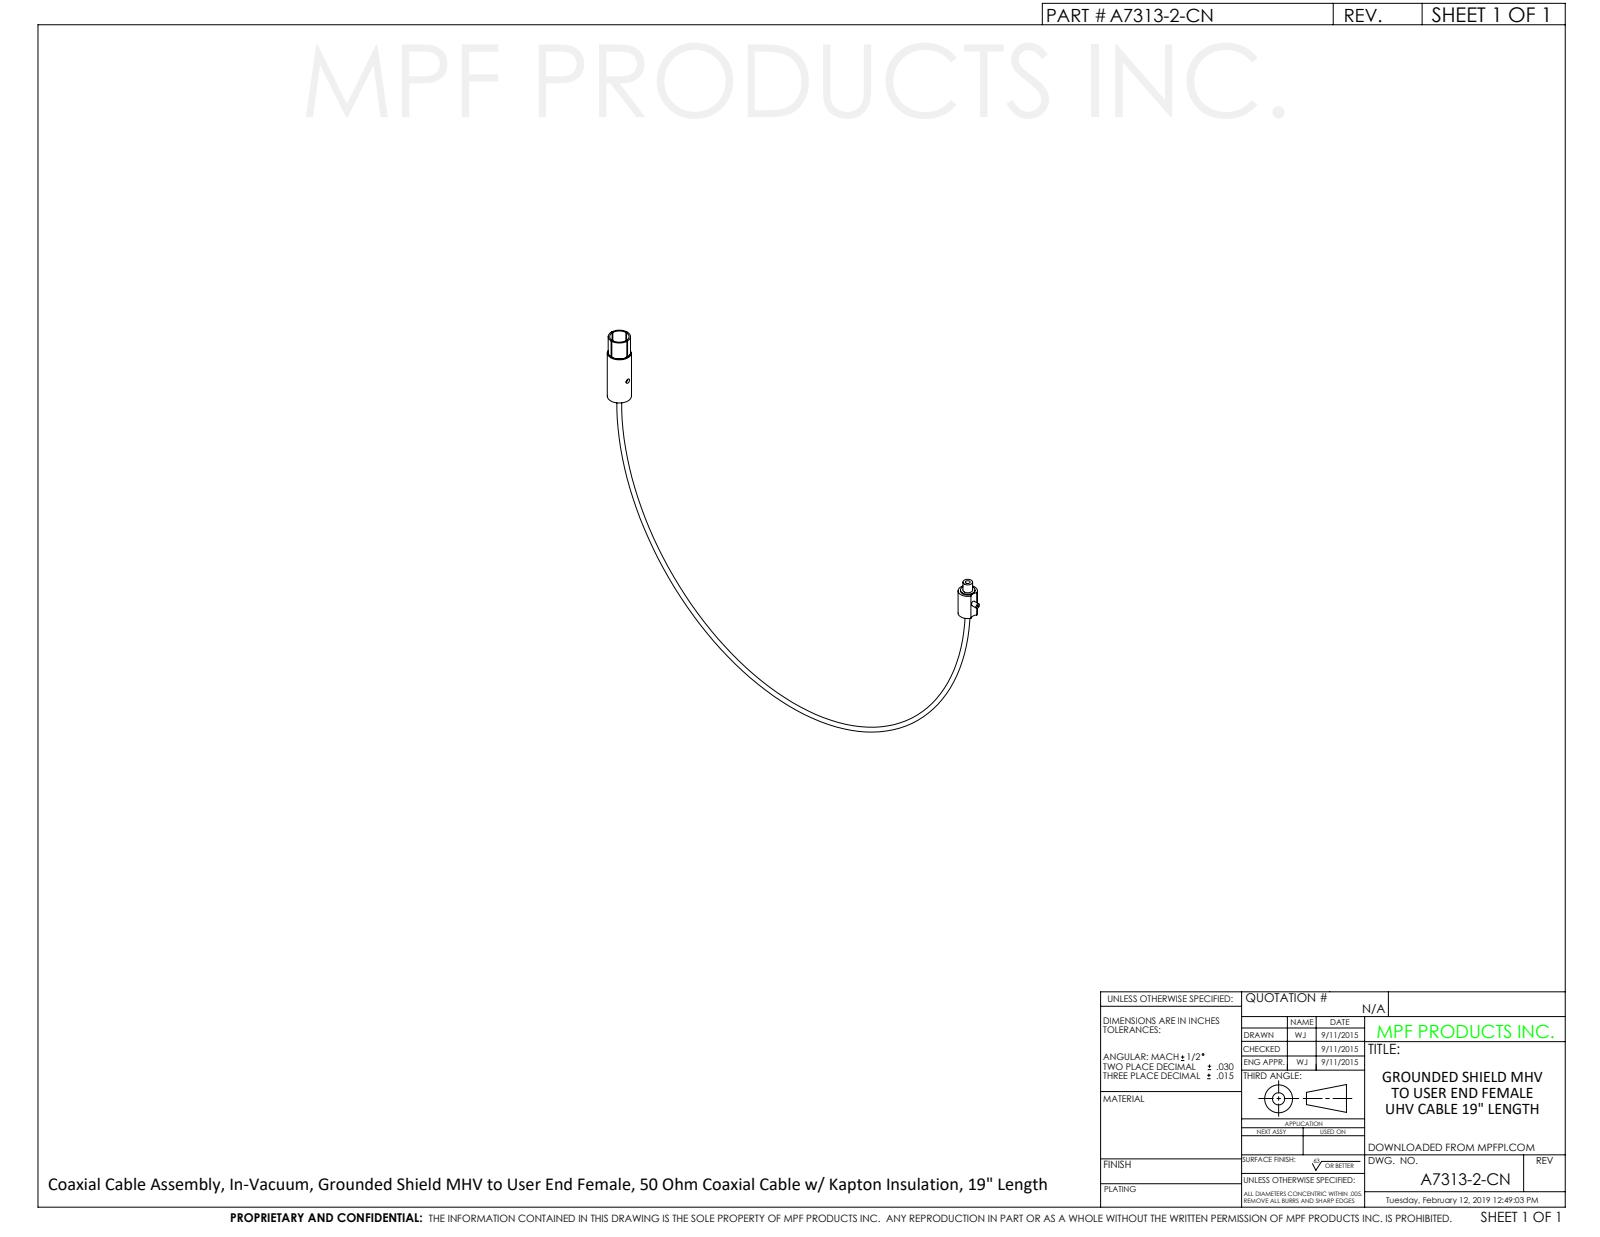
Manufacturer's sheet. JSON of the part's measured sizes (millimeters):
{"part_name": "A7313-2-CN", "step_written_by": "SolidWorks 2012 (CONFIG_CONTROL_DESIGN)", "units": "millimeters", "bodies": {"solids": 1, "faces": 58, "planar": 25, "cylindrical": 28, "other": 5}, "overall_size": [279.2, 173.6, 20.3], "volume_mm3": 15100, "surface_area_mm2": 9794, "round_holes": [[2.5, 3], [0.6, 1], [12.7, 1]], "round_bosses_or_shafts": [[20.3, 1], [19.1, 1], [18, 1], [15.2, 1], [10.2, 1], [2.8, 1], [2.6, 1]], "partial_cylinders_radius": [[3.5, 1]], "face_to_face_distances": [10.1, 18.1, 8, 48.2, 38.1, 30.1, 15.2, 5.1, 2.9, 33], "hole_center_spacings": [14.7, 258.1]}
